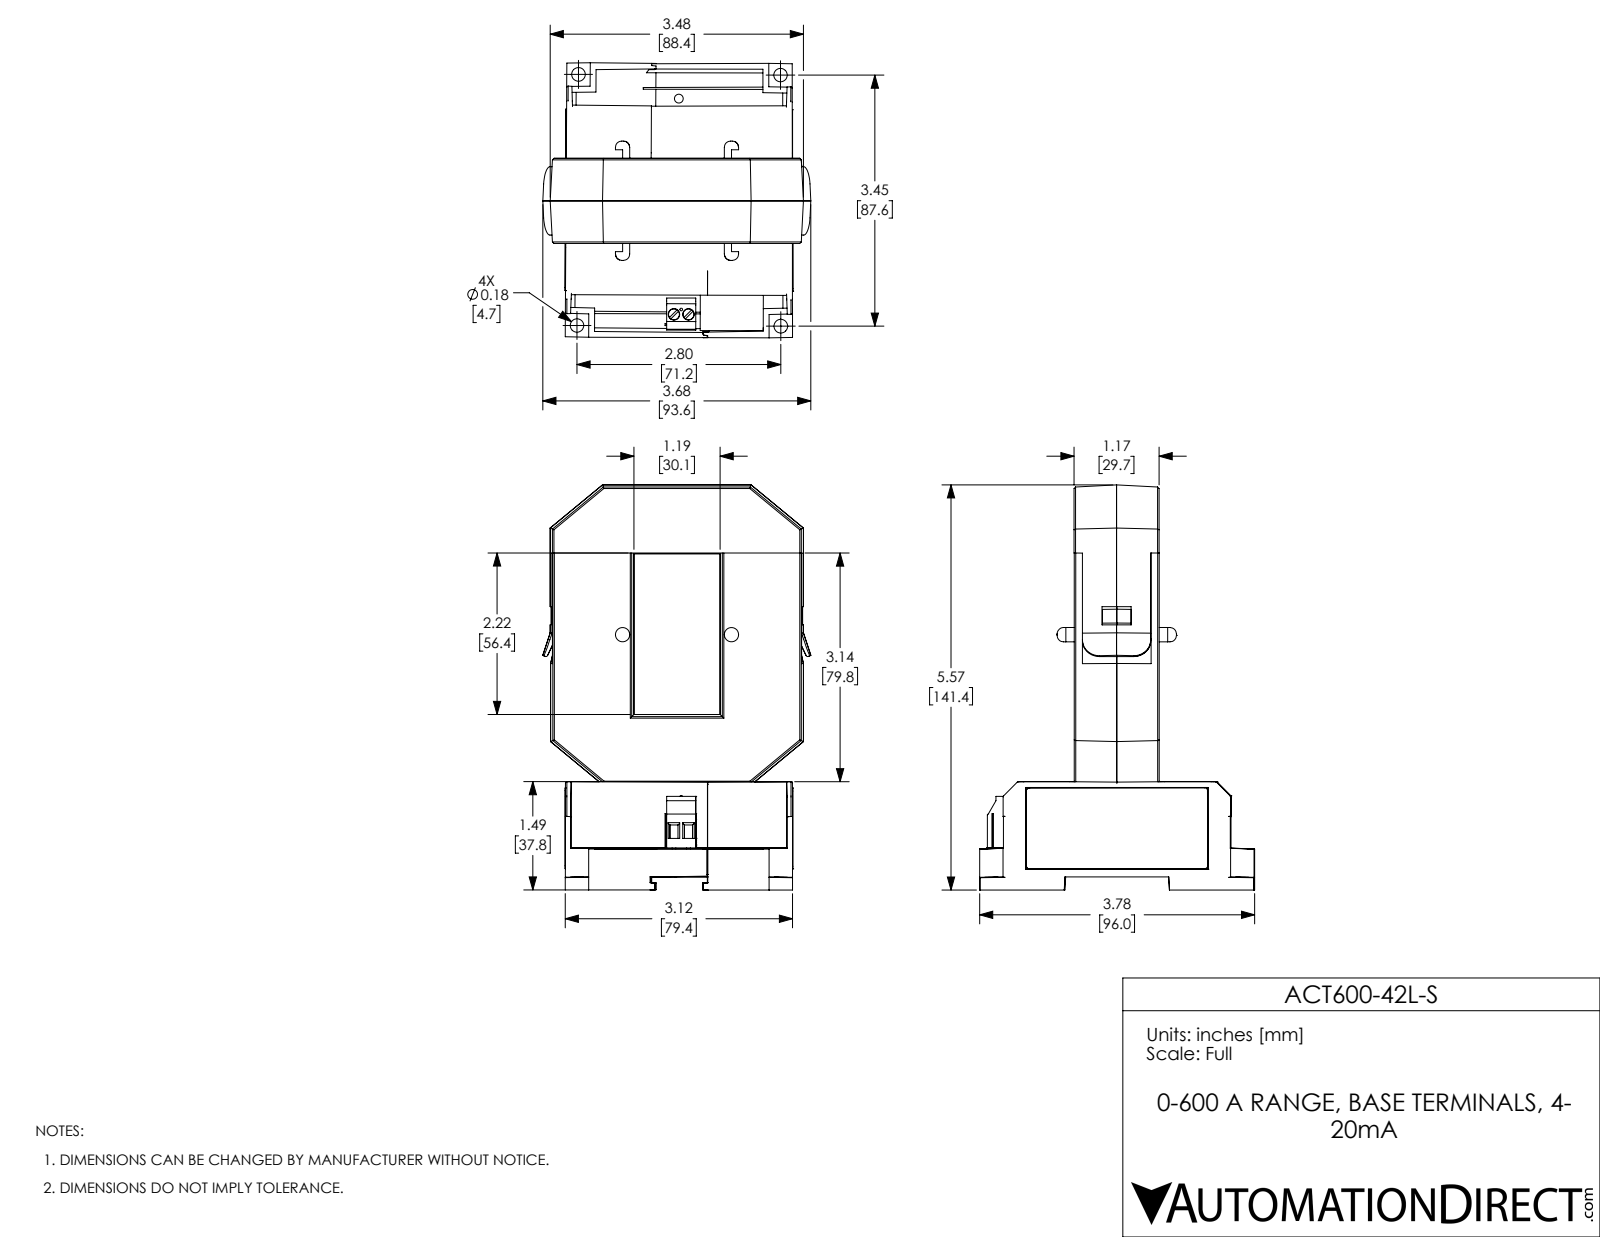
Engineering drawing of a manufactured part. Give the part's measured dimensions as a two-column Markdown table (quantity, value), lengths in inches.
| quantity | value |
| --- | --- |
| part name | ACT600-42L-S |
| STEP written by | SolidWorks 2017 (AUTOMOTIVE_DESIGN) |
| units | inches |
| bodies | 15 solids, 1439 faces (1182 planar, 144 cylindrical, 113 other) |
| overall size | 5.569 × 3.781 × 3.684 |
| volume | 7.995 in³ |
| surface area | 222.6 in² |
| round holes (diameter × count) | 0.157 × 2, 0.256 × 2 |
| round bosses / shafts (diameter × count) | 0.197 × 2, 0.15 × 2, 0.051 × 2, 0.018 × 1 |
| partial cylindrical surfaces (radius × count) | 0.02 × 30, 0.039 × 12, 0.006 × 10, 0.05 × 8, 0.025 × 6, 0.008 × 4, 0.01 × 4, 0.02 × 4 |
| main face-to-face distances | 0.071, 1.097, 1.168, 1.026, 0.081, 0.585, 0.075, 0.08, 2.328, 1.095 |
| hole center spacings | 0.2, 0.42, 1.563, 1.57, 1.581, 1.604 |
